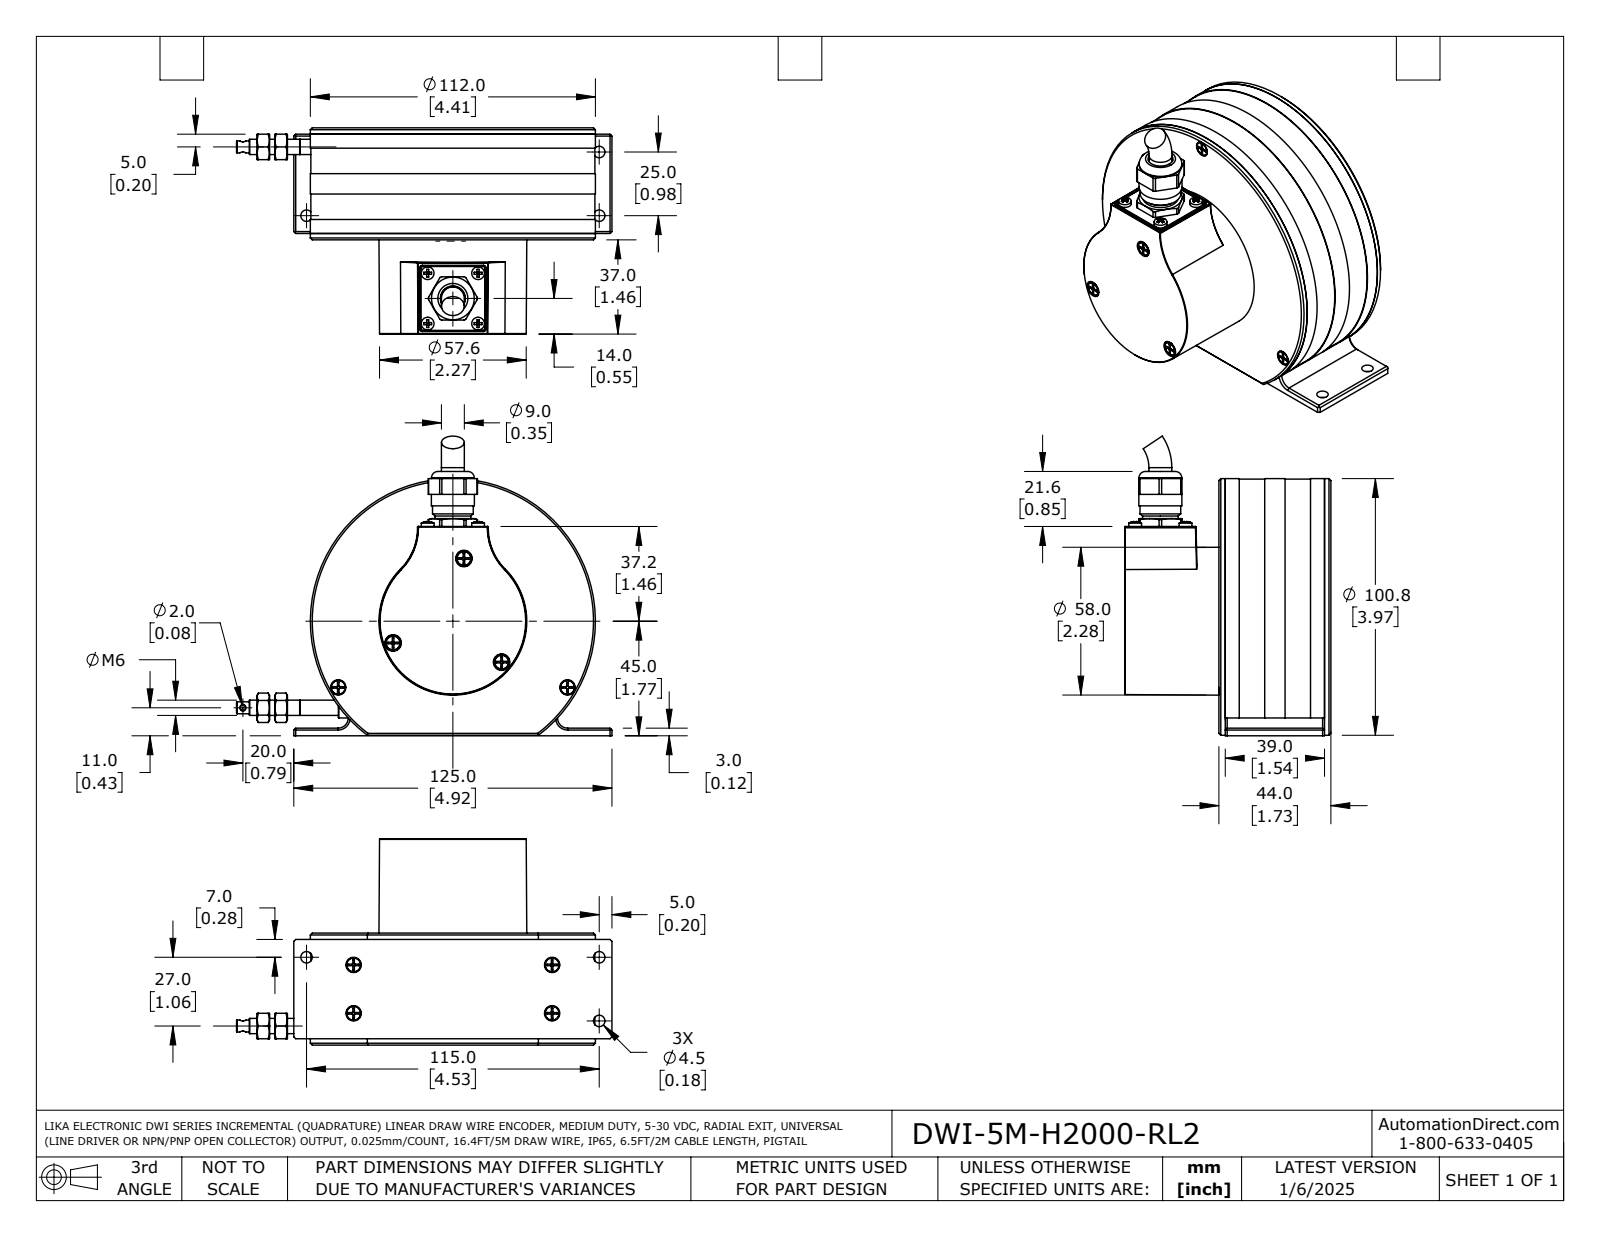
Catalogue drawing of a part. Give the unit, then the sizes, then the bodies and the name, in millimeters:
Units: millimetres
Overall size (bounding box): 147.5 × 117.7 × 81
Round holes (diameter × count): ⌀2.5 ×13, ⌀3.2 ×7, ⌀6 ×7, ⌀2 ×5, ⌀4 ×4, ⌀4.5 ×4, ⌀1.5 ×2, ⌀1.6 ×2, ⌀8 ×2, ⌀5 ×1, ⌀9.5 ×1, ⌀9.8 ×1
Round bosses / shafts (diameter × count): ⌀3 ×11, ⌀5 ×4, ⌀2.5 ×4, ⌀112 ×1, ⌀56 ×1, ⌀53.8 ×1, ⌀52 ×1, ⌀40 ×1
Partial cylindrical surfaces — rounded edges, fillets, slot ends (radius × count): R0.2 ×45, R0.2 ×33, R0.5 ×6, R1 ×6, R0.8 ×4, R4 ×2, R4.1 ×1, R50 ×1
Main face-to-face distances: 0.5, 2.5, 2, 41.5, 39.5, 34, 31.5, 43.5, 10, 1.5
Hole centre spacings: 25, 43.3, 16.5, 18.7, 12.9, 18.5, 21, 26.4
Volume: 214 300 mm³ · Surface area: 115 100 mm²
Bodies: 30 solids, 1228 faces (457 planar, 381 cylindrical, 390 other)
Part name (STEP PRODUCT): DWI-5M-H2000-RL2
STEP written by: SolidWorks 2021 (AUTOMOTIVE_DESIGN)
